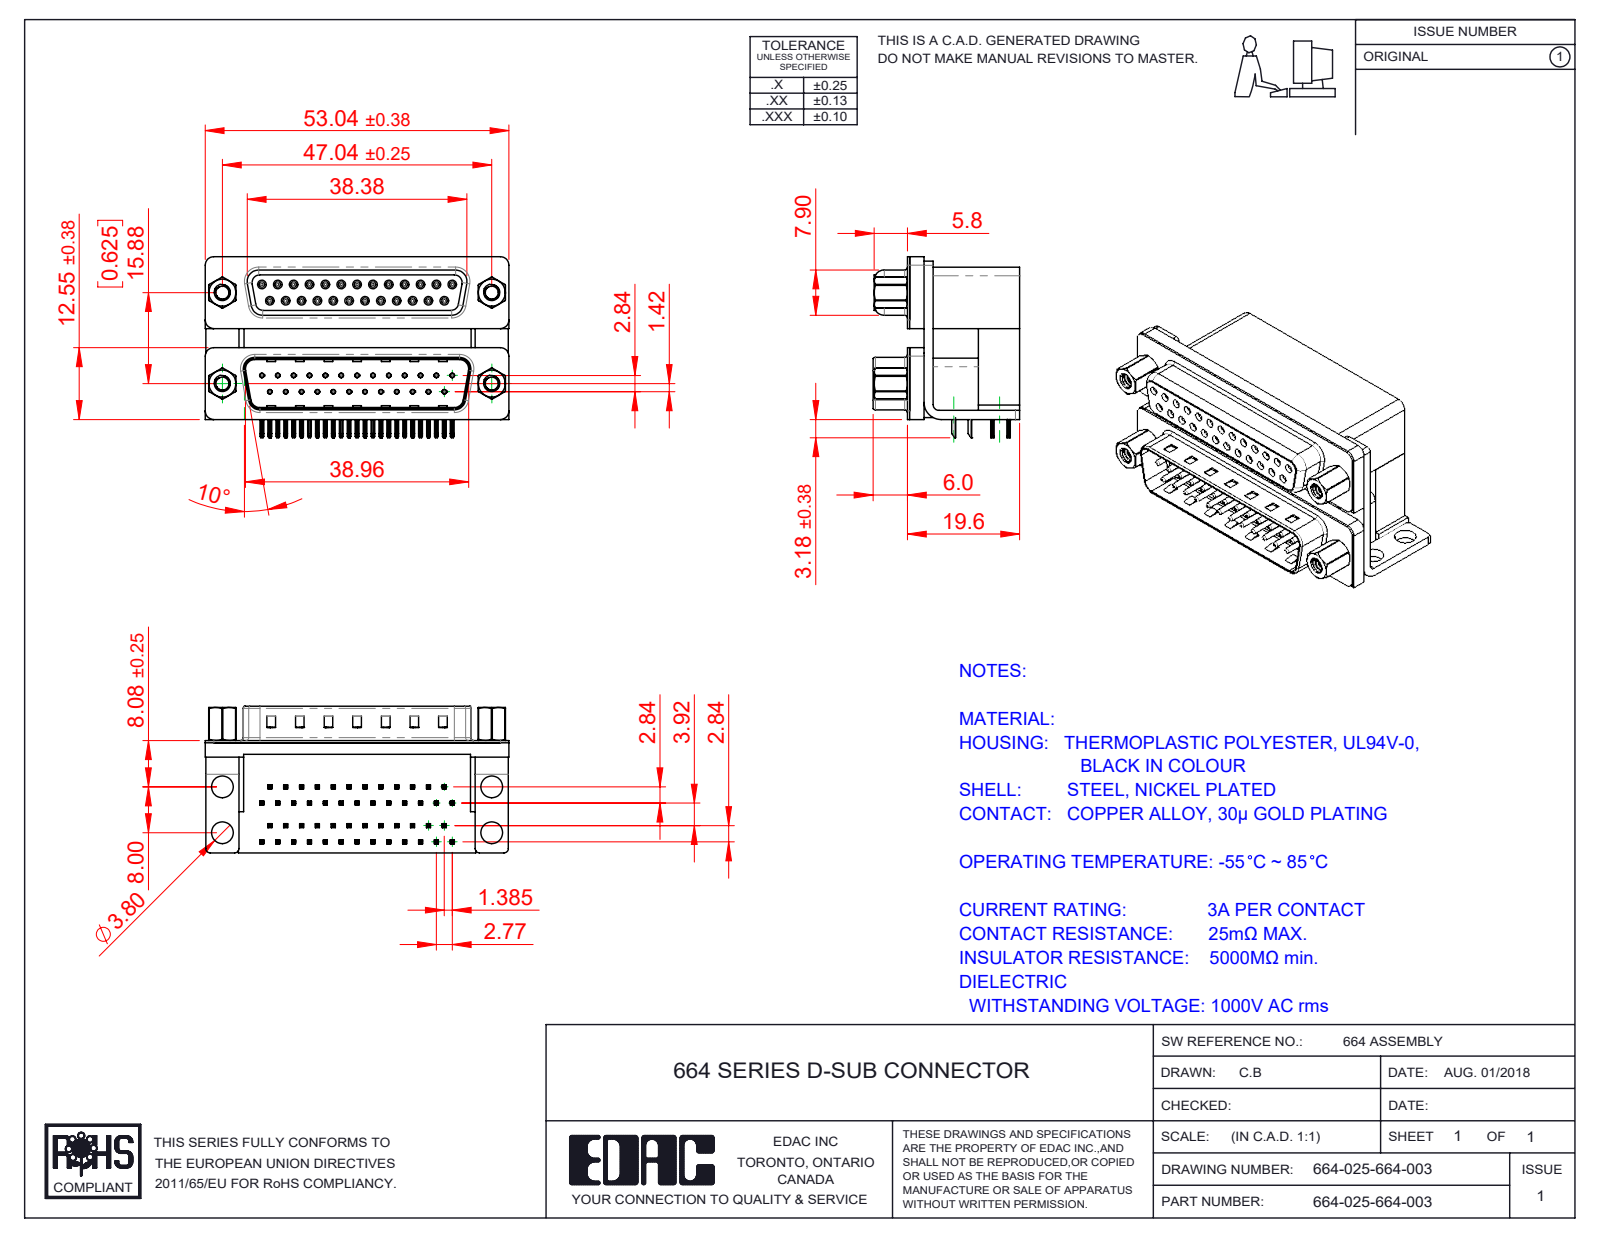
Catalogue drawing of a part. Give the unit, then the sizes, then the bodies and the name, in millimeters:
Units: millimetres
Overall size (bounding box): 53.04 × 31.61 × 25.6
Round holes (diameter × count): ⌀0.8 ×50, ⌀0.35 ×25, ⌀0.9 ×25, ⌀2.26 ×4, ⌀2.29 ×4, ⌀3.5 ×4, ⌀3.8 ×4, ⌀4 ×4, ⌀4.8 ×4, ⌀5 ×4
Round bosses / shafts (diameter × count): ⌀1.2 ×25, ⌀0.75 ×25, ⌀4.9 ×4, ⌀4.75 ×4, ⌀3.9 ×4, ⌀2.79 ×4
Partial cylindrical surfaces — rounded edges, fillets, slot ends (radius × count): R0.1 ×200, R0.15 ×100, R0.25 ×100, R0.12 ×50, R0.35 ×50, R0.34 ×25, R1.5 ×13, R0.28 ×12
Main face-to-face distances: 0.4, 19.2, 10.7, 7.2, 12, 16.7, 9.5, 2.5, 15.53, 26.23
Hole centre spacings: 2.77, 3.16, 5.54, 8.31, 11.08, 13.85, 16.62, 5.03
Volume: 21 948 mm³ · Surface area: 24 117 mm²
Bodies: 65 solids, 6455 faces (3301 planar, 1687 cylindrical, 1467 other)
Part name (STEP PRODUCT): 664 Contact Top Lower; 664 Housing Spacer_25 Contacts L; 664 Threaded Rivet_4-40; 664 Shell Plug_25 Contacts (+8 more)
STEP written by: SolidWorks 2020 (CONFIG_CONTROL_DESIGN)
